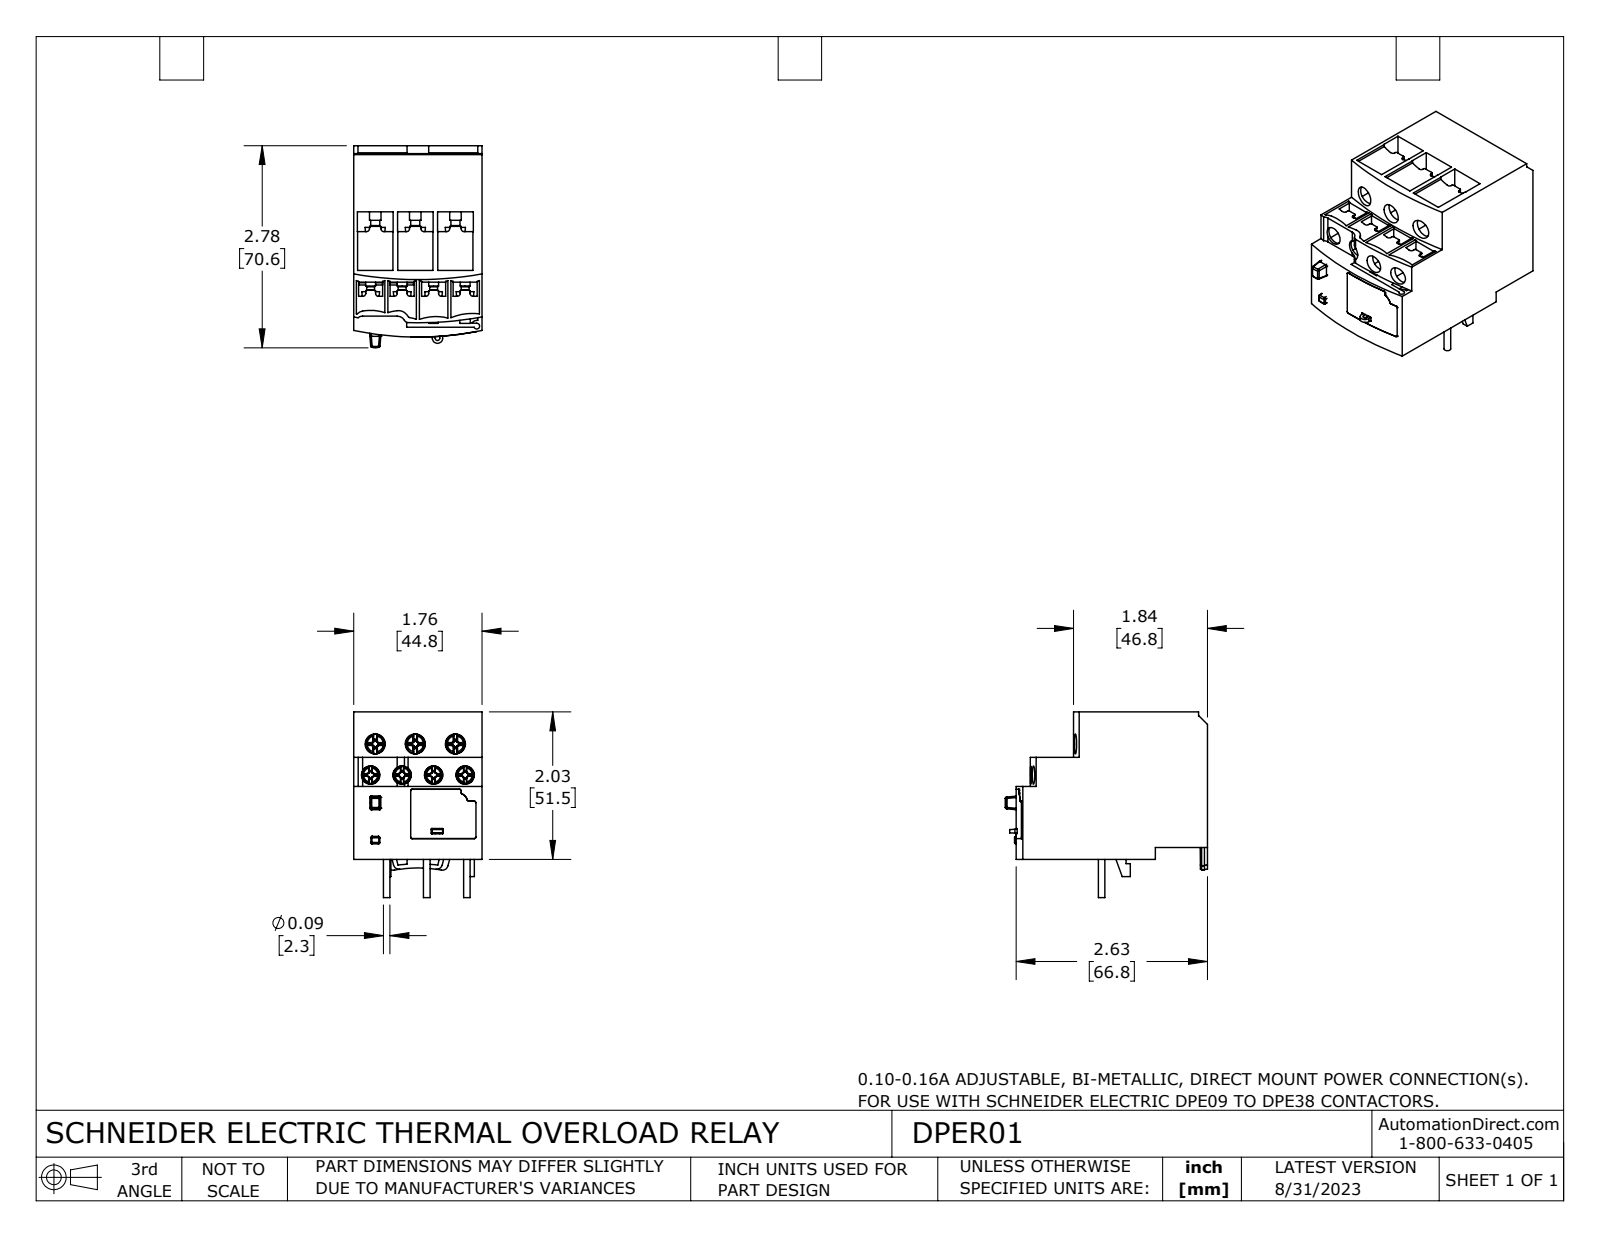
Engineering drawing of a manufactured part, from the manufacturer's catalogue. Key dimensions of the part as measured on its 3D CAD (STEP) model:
Part name (STEP PRODUCT): DPER01
STEP written by: SolidWorks 2021 (CONFIG_CONTROL_DESIGN)
Units: inches
Bodies: 16 solids, 1212 faces (676 planar, 269 cylindrical, 267 other)
Overall size (bounding box): 2.778 × 2.553 × 1.764
Volume: 6.953 in³ · Surface area: 47.15 in²
Round holes (diameter × count): ⌀0.252 ×4, ⌀0.276 ×3, ⌀0.079 ×2, ⌀0.118 ×2, ⌀0.059 ×1, ⌀0.244 ×1
Round bosses / shafts (diameter × count): ⌀0.091 ×12, ⌀0.138 ×4, ⌀0.108 ×4, ⌀0.157 ×3, ⌀0.154 ×3, ⌀0.124 ×3, ⌀0.118 ×1, ⌀0.107 ×1
Partial cylindrical surfaces — rounded edges, fillets, slot ends (radius × count): R0.02 ×52, R0.039 ×22, R0.004 ×19, R0.012 ×8, R0.008 ×6, R0.63 ×6, R0.079 ×4, R0.024 ×2
Main face-to-face distances: 1.764, 0.165, 2.028, 1.863, 0.909, 0.551, 0.618, 1.409, 1.245, 2.497
Hole centre spacings: 0.433, 0.551, 0.866, 0.334, 0.381, 0.404, 0.422, 0.449
